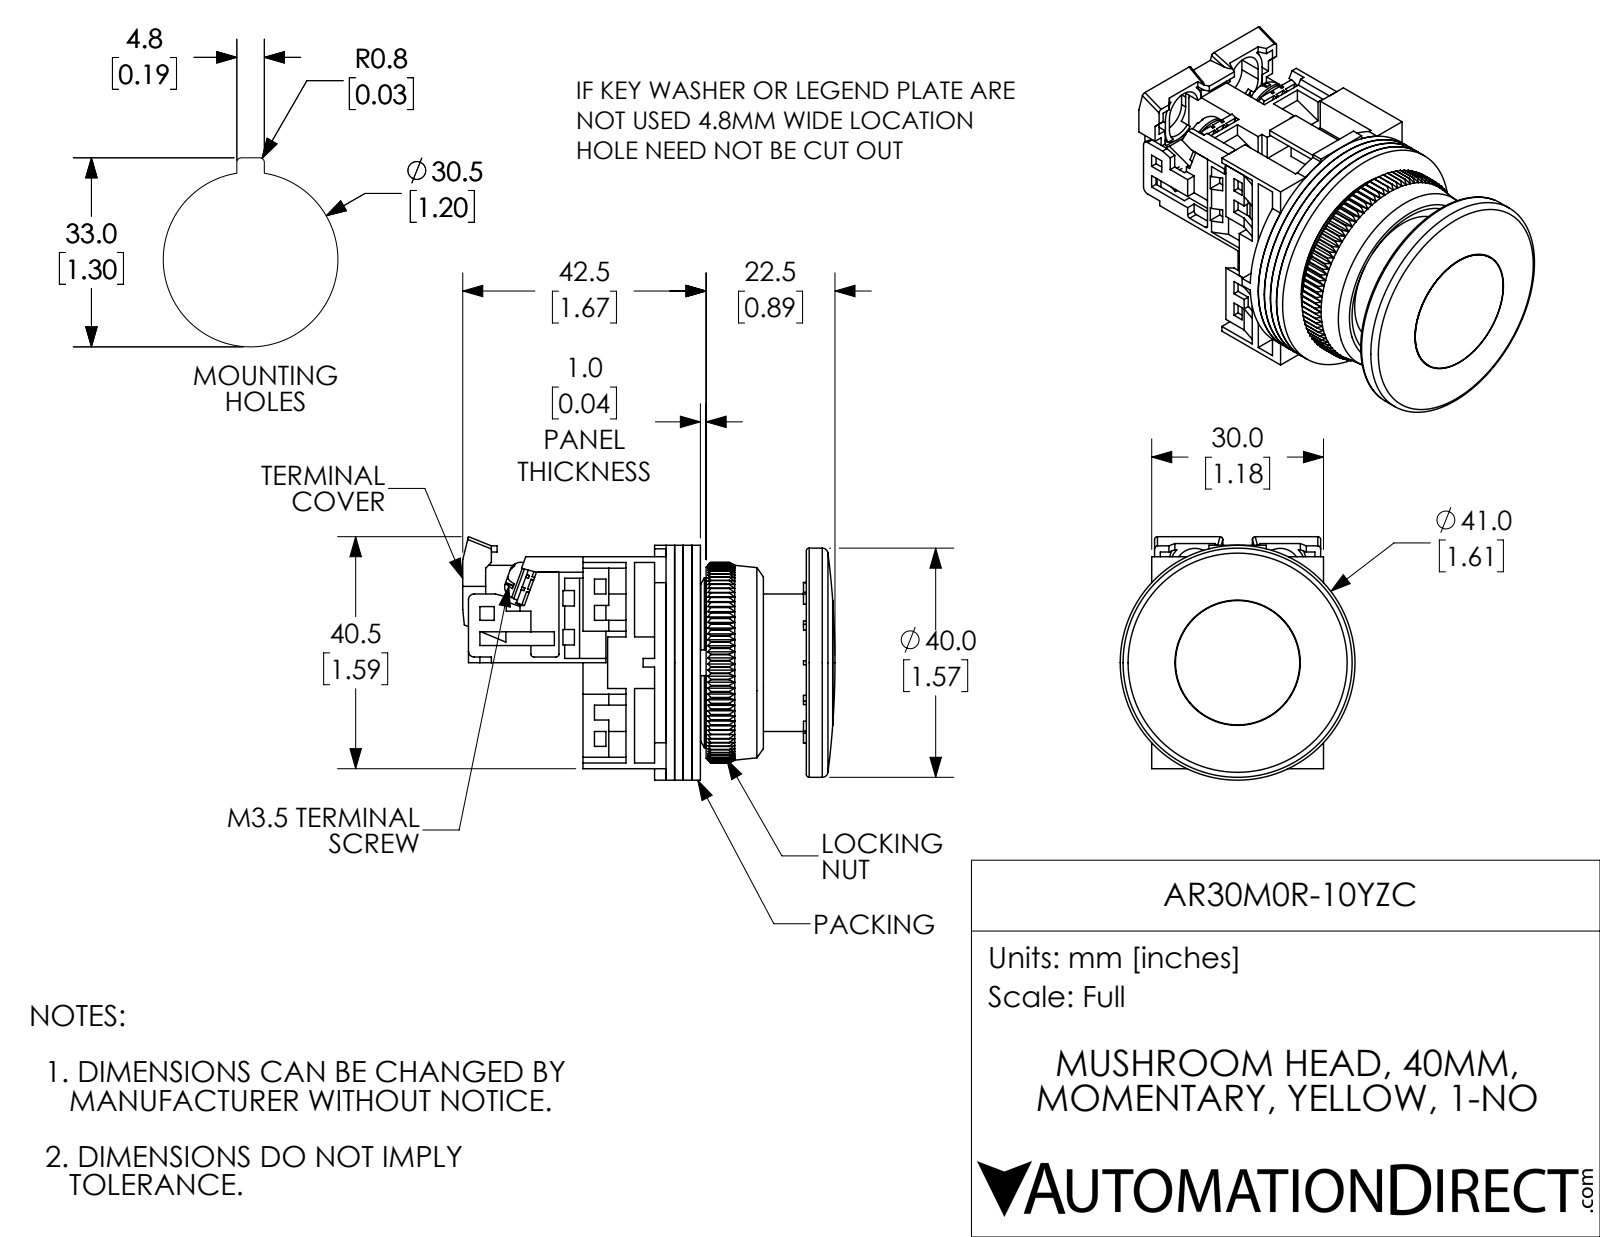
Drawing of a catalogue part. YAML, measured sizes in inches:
part_name: "AR30M0R-10YZC"
step_written_by: "SolidWorks 2017 (AUTOMOTIVE_DESIGN)"
units: inches
bodies: {solids: 15, faces: 1278, planar: 819, cylindrical: 260, other: 199}
overall_size: [2.559, 1.673, 1.614]
volume: 2.225
surface_area: 48.33
round_holes:
  - {diameter: 0.138, count: 4}
  - {diameter: 0.142, count: 2}
  - {diameter: 0.118, count: 1}
  - {diameter: 0.709, count: 1}
  - {diameter: 0.945, count: 1}
  - {diameter: 1.122, count: 1}
  - {diameter: 1.252, count: 1}
  - {diameter: 1.417, count: 1}
round_bosses_or_shafts:
  - {diameter: 0.26, count: 2}
  - {diameter: 0.138, count: 2}
  - {diameter: 1.614, count: 1}
  - {diameter: 1.575, count: 1}
  - {diameter: 1.181, count: 1}
  - {diameter: 0.854, count: 1}
partial_cylinders:
  - {radius: 0.059, count: 8}
  - {radius: 0.02, count: 6}
  - {radius: 0.039, count: 2}
  - {radius: 0.138, count: 2}
  - {radius: 0.177, count: 2}
  - {radius: 0.118, count: 1}
  - {radius: 0.398, count: 1}
  - {radius: 0.449, count: 1}
face_to_face_distances: [0.059, 0.118, 0.177, 0.039, 0.079, 0.689, 0.728, 0.866, 0.807, 1.417]
hole_center_spacings: [0.579, 0.61]
